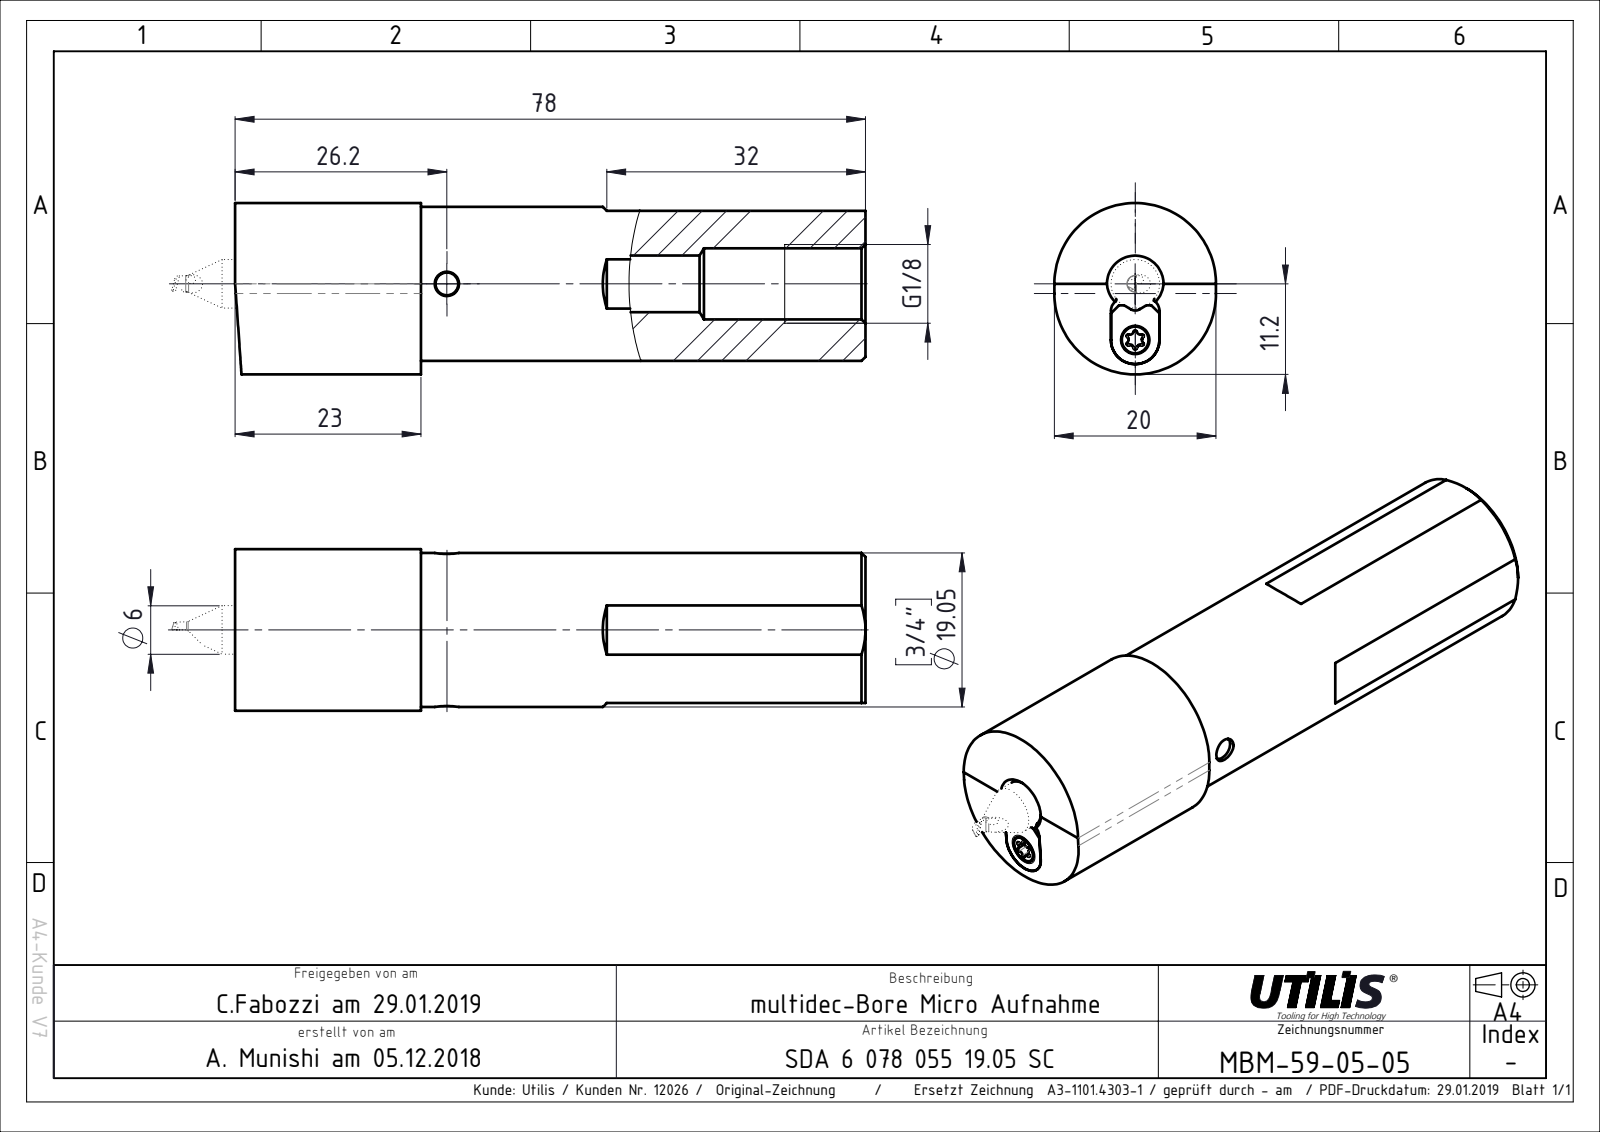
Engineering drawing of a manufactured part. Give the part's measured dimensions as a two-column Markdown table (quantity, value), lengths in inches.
| quantity | value |
| --- | --- |
| part name | UTP AblageMBM-59-05-05 |
| STEP written by | SolidWorks 2018 (CONFIG_CONTROL_DESIGN) |
| units | inches |
| bodies | 1 solid, 49 faces (13 planar, 18 cylindrical, 18 other) |
| overall size | 3.071 × 0.835 × 0.787 |
| volume | 1.191 in³ |
| surface area | 11.49 in² |
| round holes (diameter × count) | 0.118 × 1, 0.13 × 1, 0.236 × 1, 0.276 × 1, 0.346 × 1 |
| round bosses / shafts (diameter × count) | 0.75 × 1 |
| partial cylindrical surfaces (radius × count) | 0.394 × 2, 0.118 × 1 |
| main face-to-face distances | 3.071, 0.276, 0.512, 0.906, 2.165, 0.237, 0.236, 0.474, 0.346, 0.038 |
